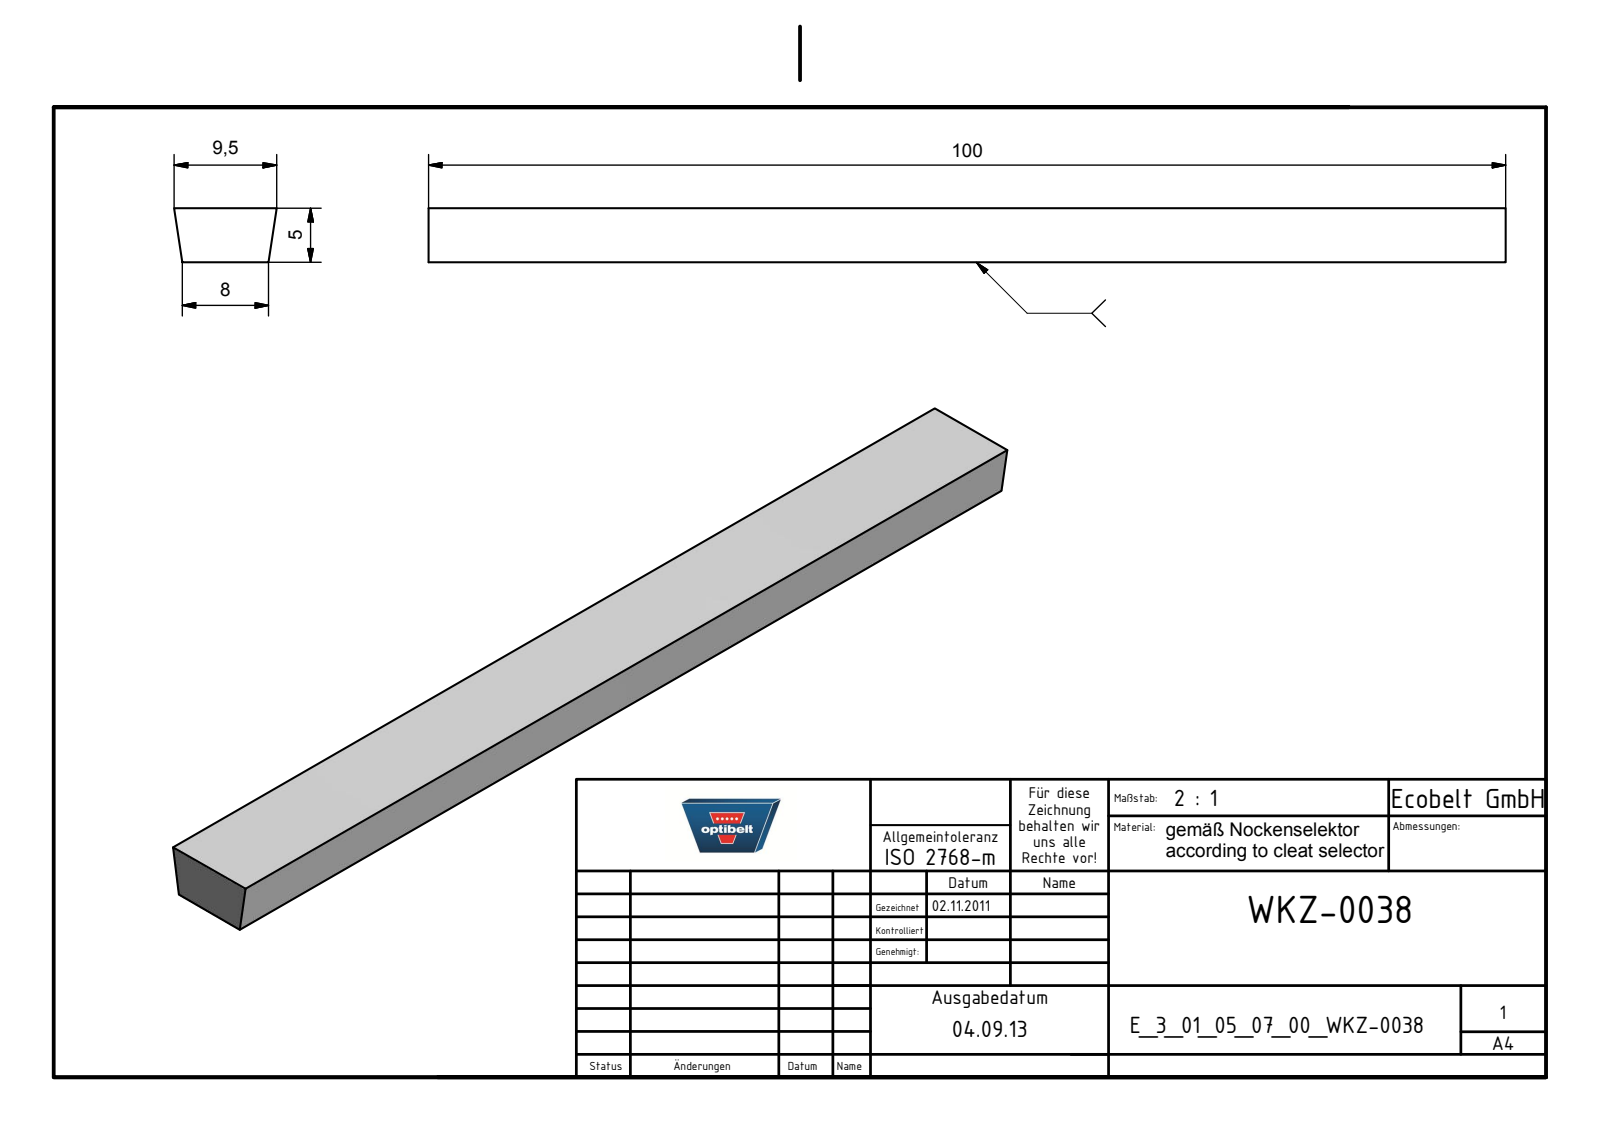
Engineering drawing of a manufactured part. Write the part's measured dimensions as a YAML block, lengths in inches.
part_name: "E_3_01_05_07_00_WKZ-0038"
step_written_by: "Autodesk Inventor 2021 (AUTOMOTIVE_DESIGN)"
units: inches
bodies: {solids: 1, faces: 6, planar: 6, cylindrical: 0, other: 0}
overall_size: [3.937, 0.374, 0.197]
volume: 0.267
surface_area: 4.416
face_to_face_distances: [0.197, 3.937]
